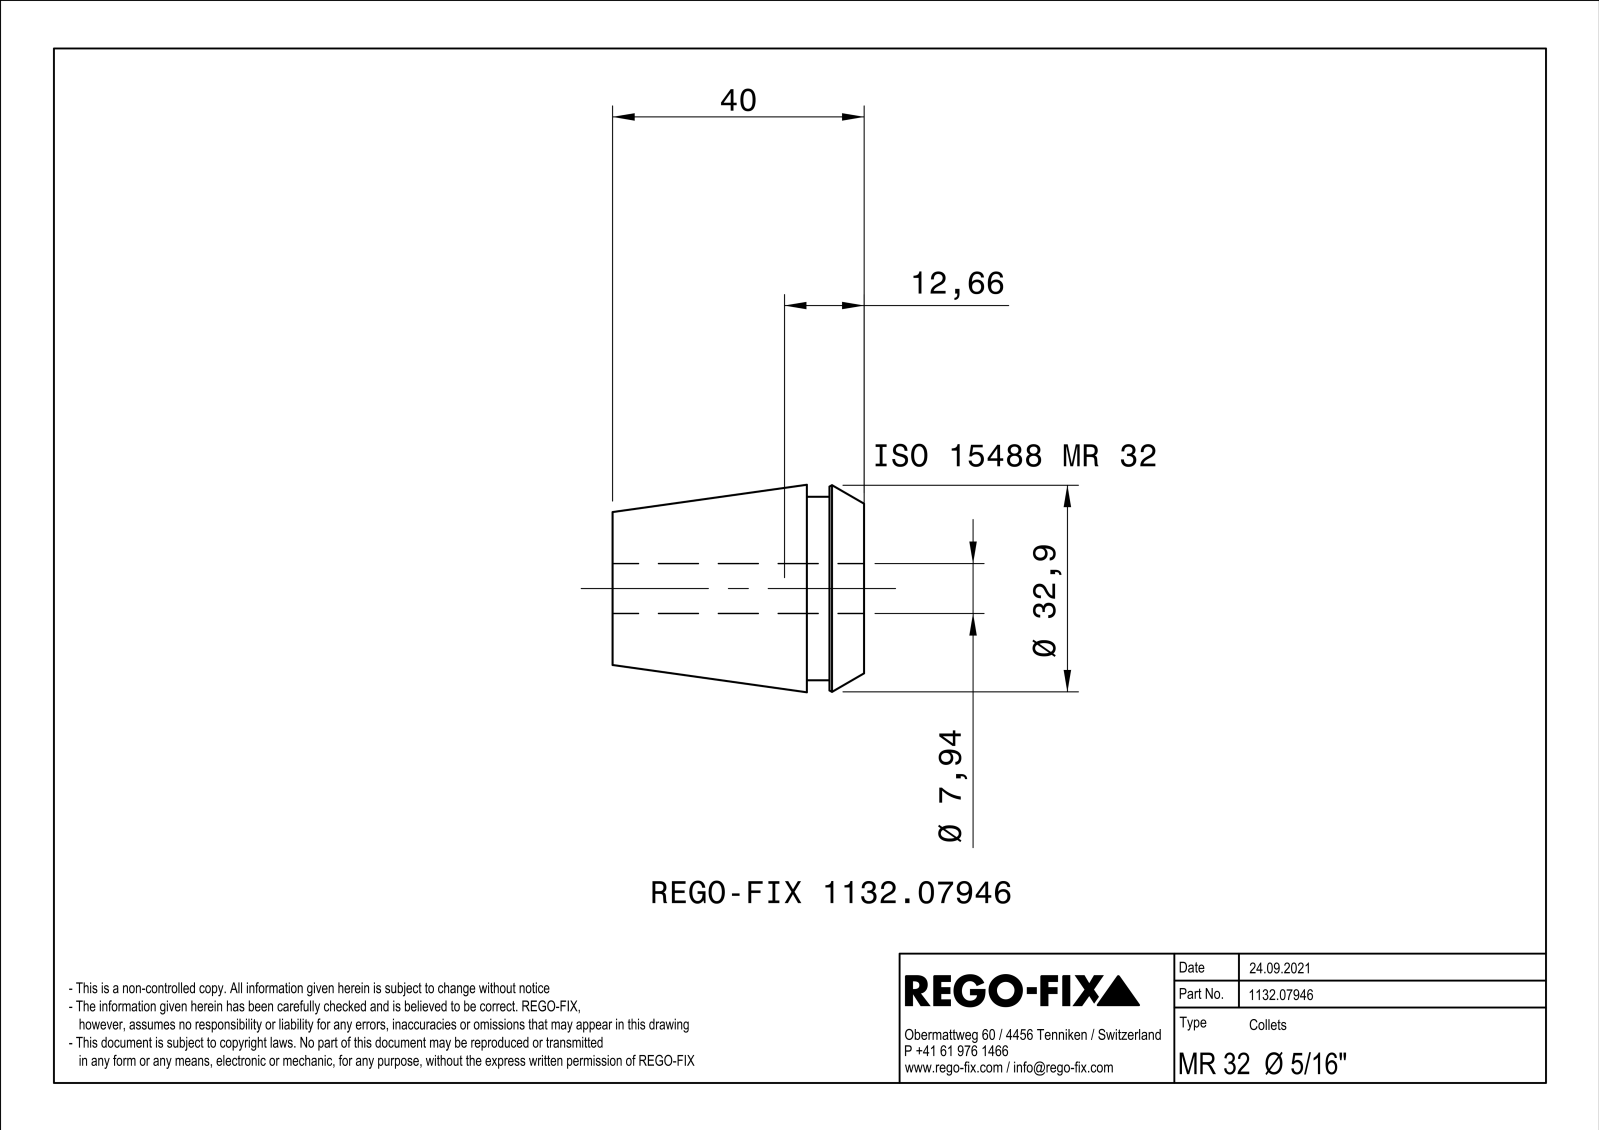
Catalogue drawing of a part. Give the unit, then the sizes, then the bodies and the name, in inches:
Units: inches
Overall size (bounding box): 1.575 × 1.299 × 1.299
Round holes (diameter × count): ⌀0.591 ×1
Round bosses / shafts (diameter × count): ⌀1.15 ×1
Partial cylindrical surfaces — rounded edges, fillets, slot ends (radius × count): R0.016 ×13, R0.156 ×1
Main face-to-face distances: 0.031, 0.032, 0.031, 1.575, 0.358, 1.217, 0.217, 0.142, 1.358, 0.984
Volume: 1.159 in³ · Surface area: 22.23 in²
Bodies: 1 solid, 256 faces (88 planar, 48 cylindrical, 120 other)
Part name (STEP PRODUCT): NOCUT
STEP written by: SIEMENS PLM Software Solid Edge ST10 (AUTOMOTIVE_DESIGN)
